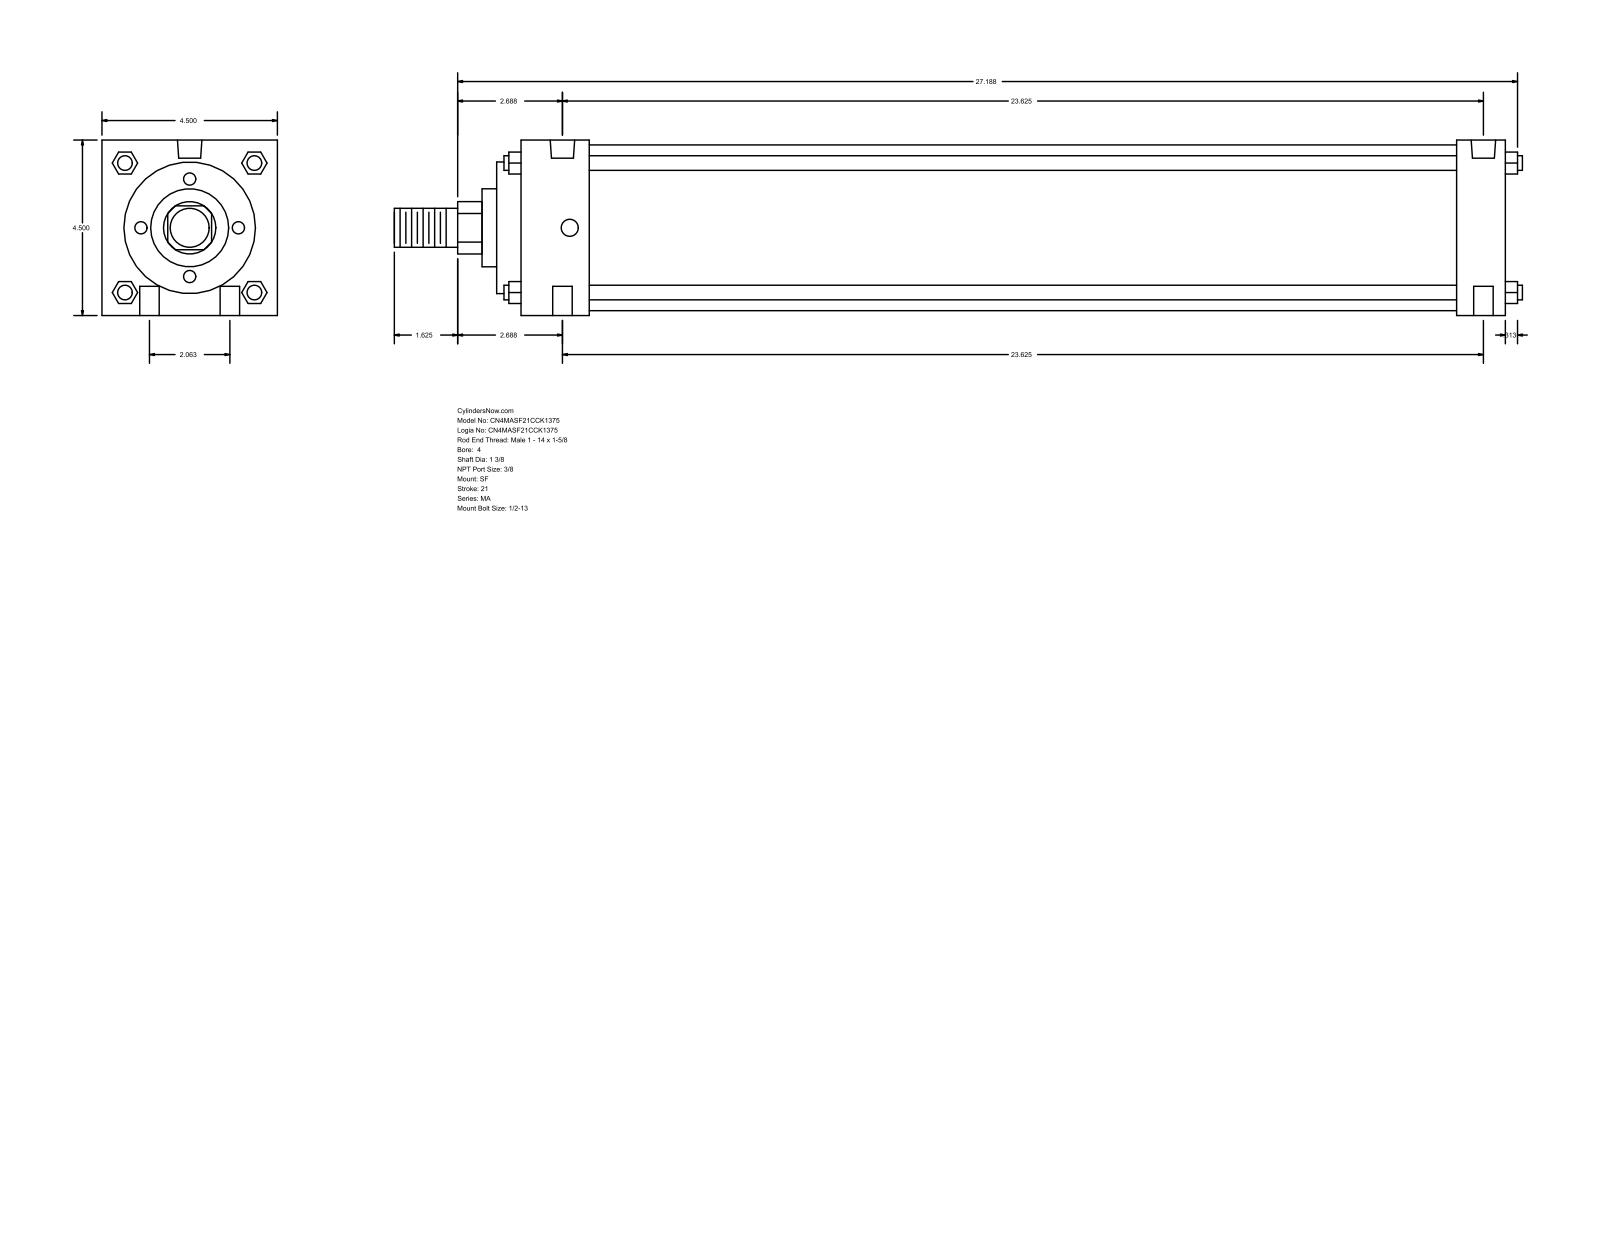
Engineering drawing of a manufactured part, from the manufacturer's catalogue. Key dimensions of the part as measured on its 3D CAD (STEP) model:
Part name (STEP PRODUCT): MA_SF__0400_1.375
STEP written by: GSSL Pune (CONFIG_CONTROL_DESIGN)
Units: millimetres
Bodies: 0 solids, 126 faces (95 planar, 31 cylindrical, 0 other)
Overall size (bounding box): 735.01 × 114.3 × 114.3
Round holes (diameter × count): ⌀12.7 ×4, ⌀11.11 ×2, ⌀15.93 ×2
Round bosses / shafts (diameter × count): ⌀9.53 ×4, ⌀107.95 ×1, ⌀85.72 ×1, ⌀50.8 ×1, ⌀34.92 ×1, ⌀25.4 ×1
Partial cylindrical surfaces — rounded edges, fillets, slot ends (radius × count): R17.06 ×1
Main face-to-face distances: 114.3, 641.35, 657.22, 15.87, 625.48, 609.61, 31.74, 60.32, 44.45, 565.16
Hole centre spacings: 26.19, 600.65, 600.08, 52.38, 602.36, 590.55
